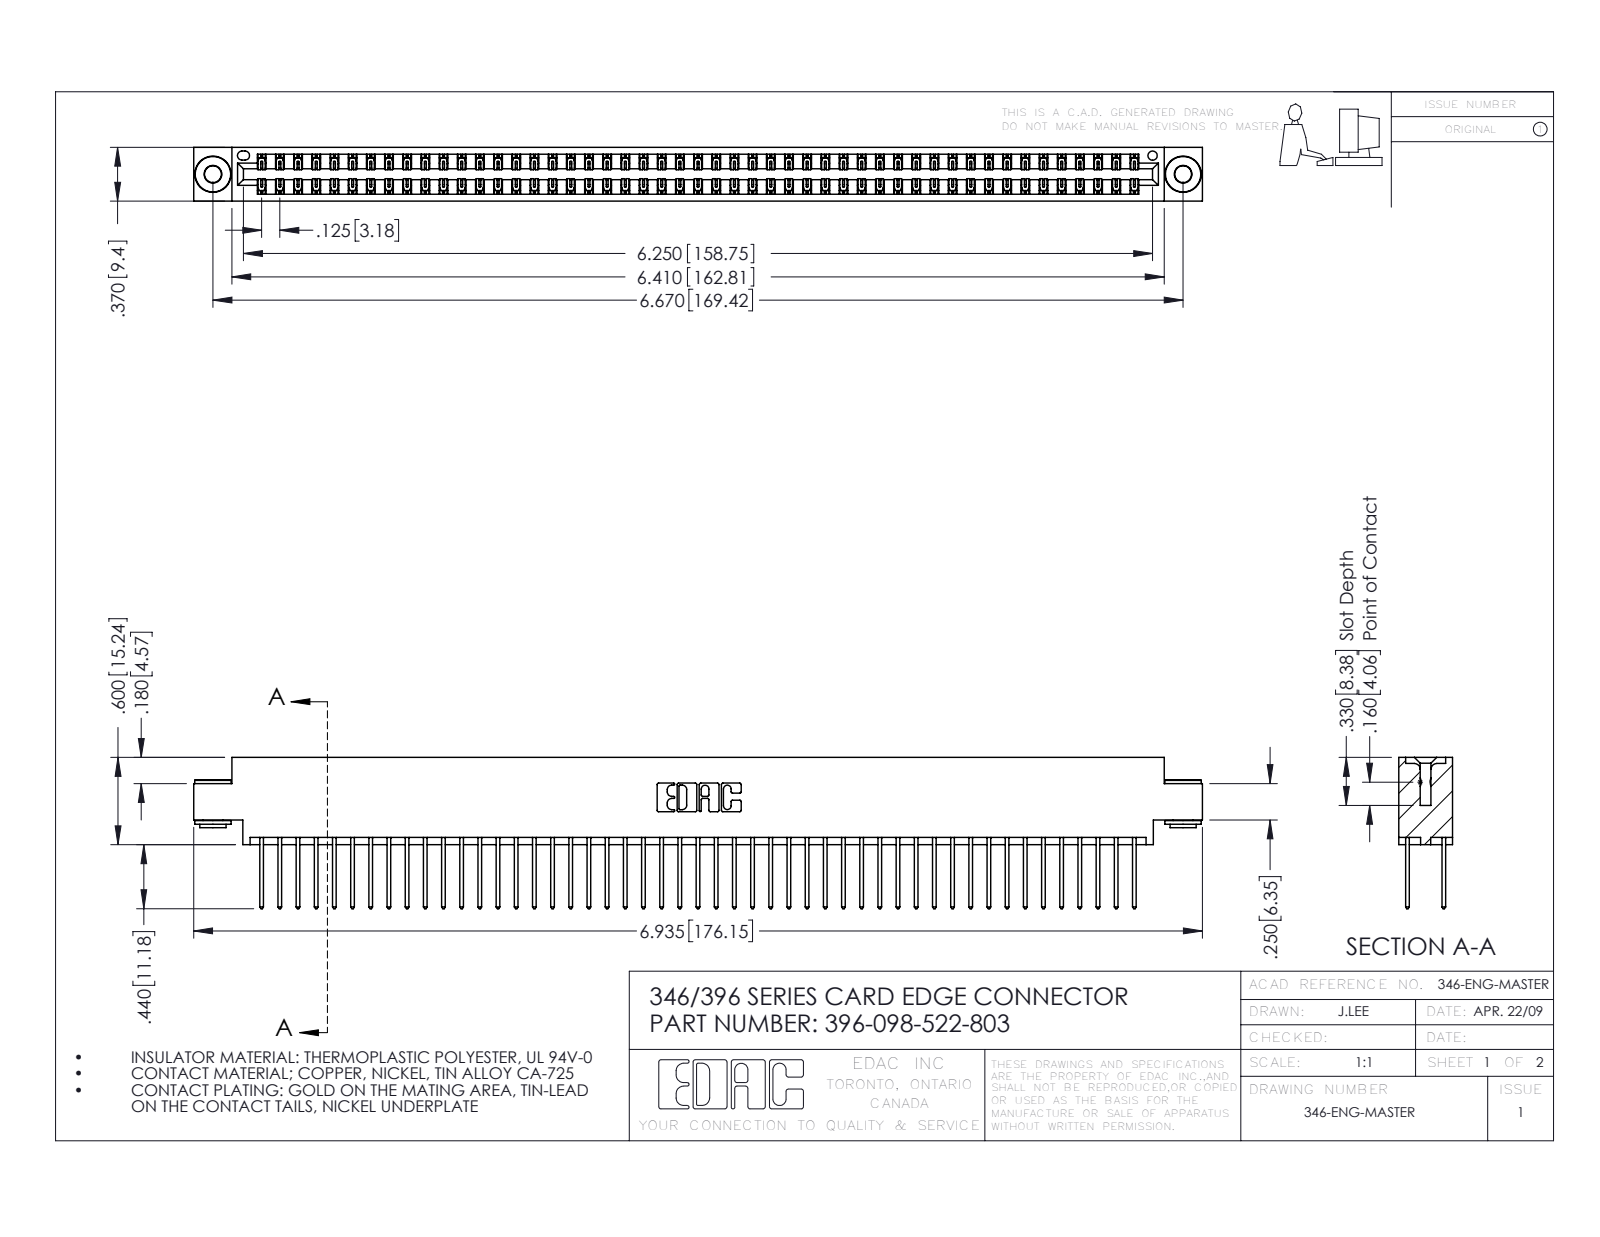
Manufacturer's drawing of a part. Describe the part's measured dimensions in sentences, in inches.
The part is named "345-250-002_345-250-002-102; 396-098-522-803; 345-292-001_345-293-122; 346 Part_0.170 Offset - 0.156 Dia-TH". Its 3-D file was written by "SolidWorks 2016 (CONFIG_CONTROL_DESIGN)". It is 101 solids with 5260 faces: 3520 planar, 1732 cylindrical and 8 other. Overall it measures 6.935 by 1.04 by 0.37 inches. Its volume is 1.059 cubic inches and its surface area 39.54 square inches. Round holes: 2 of diameter 0.116, 2 of diameter 0.156, 1 of diameter 0.064. Round bosses or shafts: 2 of diameter 0.25, 2 of diameter 0.18, 2 of diameter 0.136. Partial cylindrical surfaces (rounded edges, fillets, slot ends): 147 of radius 0.006, 98 of radius 0.01, 22 of radius 0.01, 6 of radius 0.007, 6 of radius 0.031, 3 of radius 0.026, 2 of radius 0.014, 2 of radius 0.022. The main face-to-face distances are 0.048, 0.322, 0.25, 0.37, 0.025, 0.072, 0.298, 0.275, 0.148, 0.222. The hole center spacings are 0.246, 6.461, 6.67.
